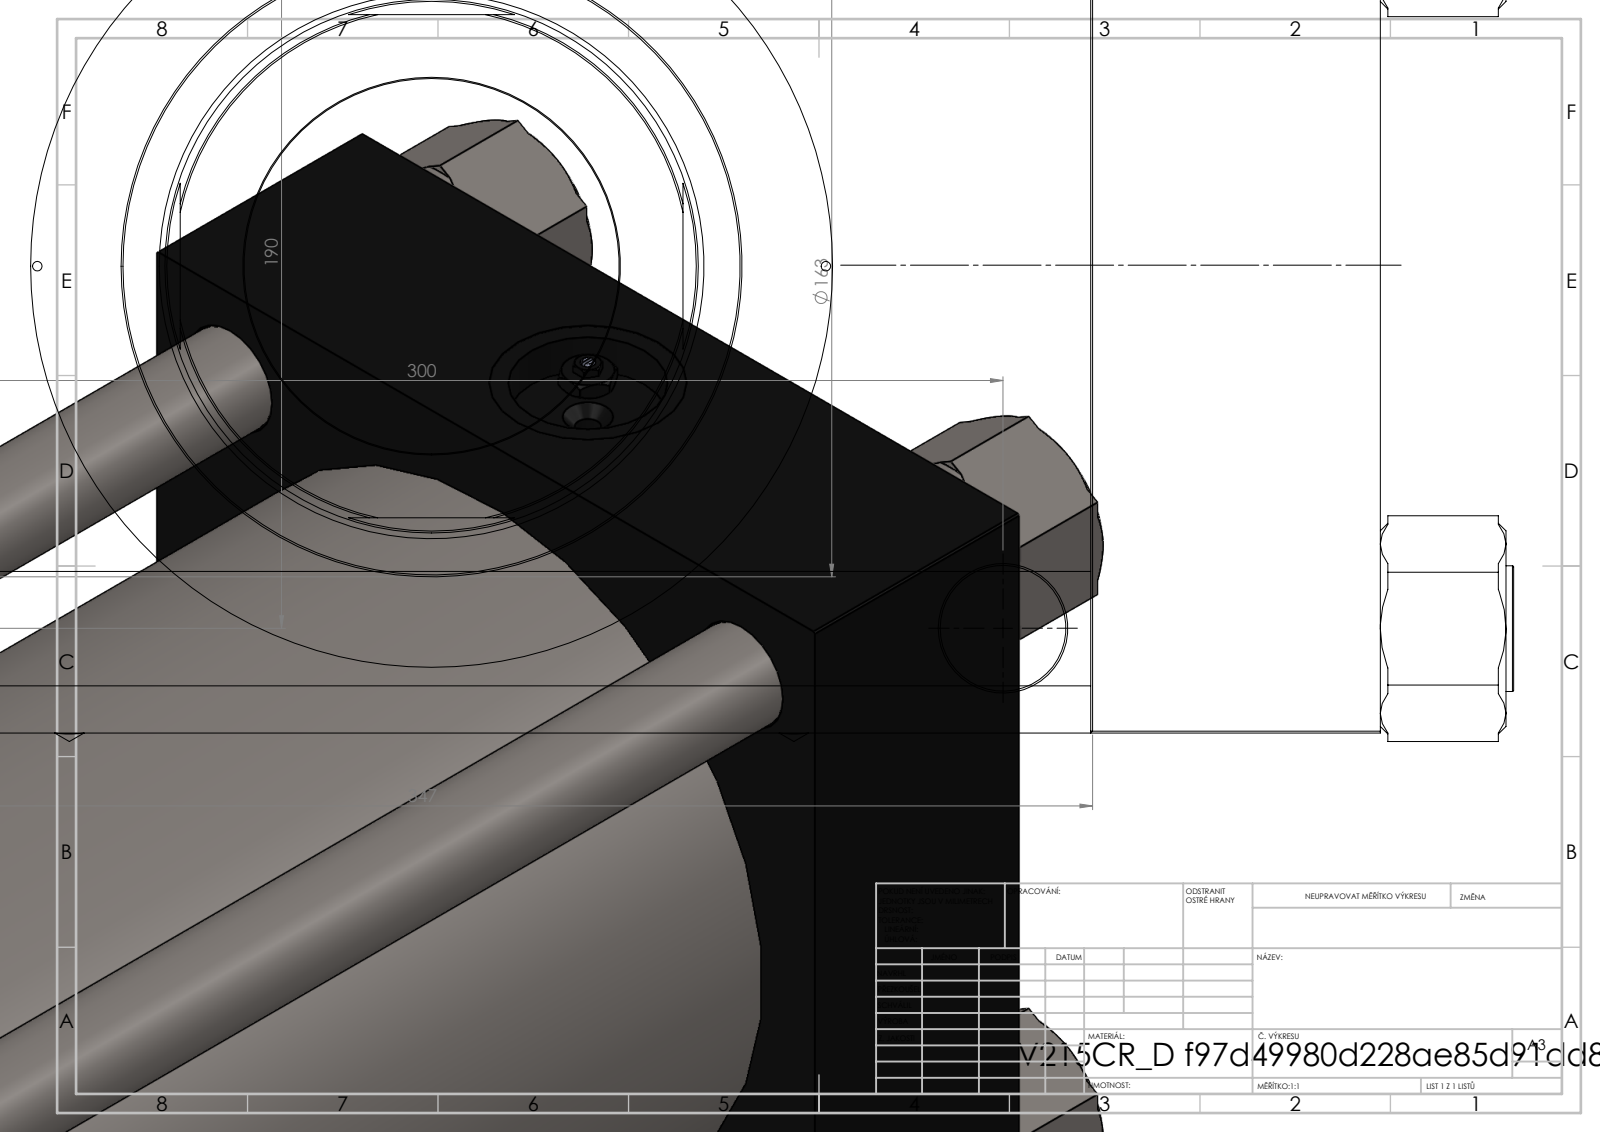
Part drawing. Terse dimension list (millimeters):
name: V215CR_D_Body; V215_VC_A; V215CR_VCP_D; Zatka_pro_OIL_PORT (+2 more)
written by: SolidWorks 2019 (CONFIG_CONTROL_DESIGN)
unit: mm
bodies: 13 solids, 1254 faces (593 planar, 101 cylindrical, 560 other)
size: 1136 × 347 × 254.22
volume: 30 590 000 mm³; area: 2 772 000 mm²
holes: 4× ⌀30, 4× ⌀33, 4× ⌀41.92, 4× ⌀52, 3× ⌀7, 2× ⌀2.5, 1× ⌀98.5, 1× ⌀140, 1× ⌀143, 1× ⌀146, 1× ⌀200, 1× ⌀210.5
bosses: 4× ⌀33, 1× ⌀206, 1× ⌀163
rounds: 1× R68
face distances: 76, 968, 892, 245, 1044, 1025.74, 949.74, 57.74, 18.26, 51
hole spacings: 54.9, 95.47, 105.77, 134.49, 177.55, 190.2, 197.87, 220.2
